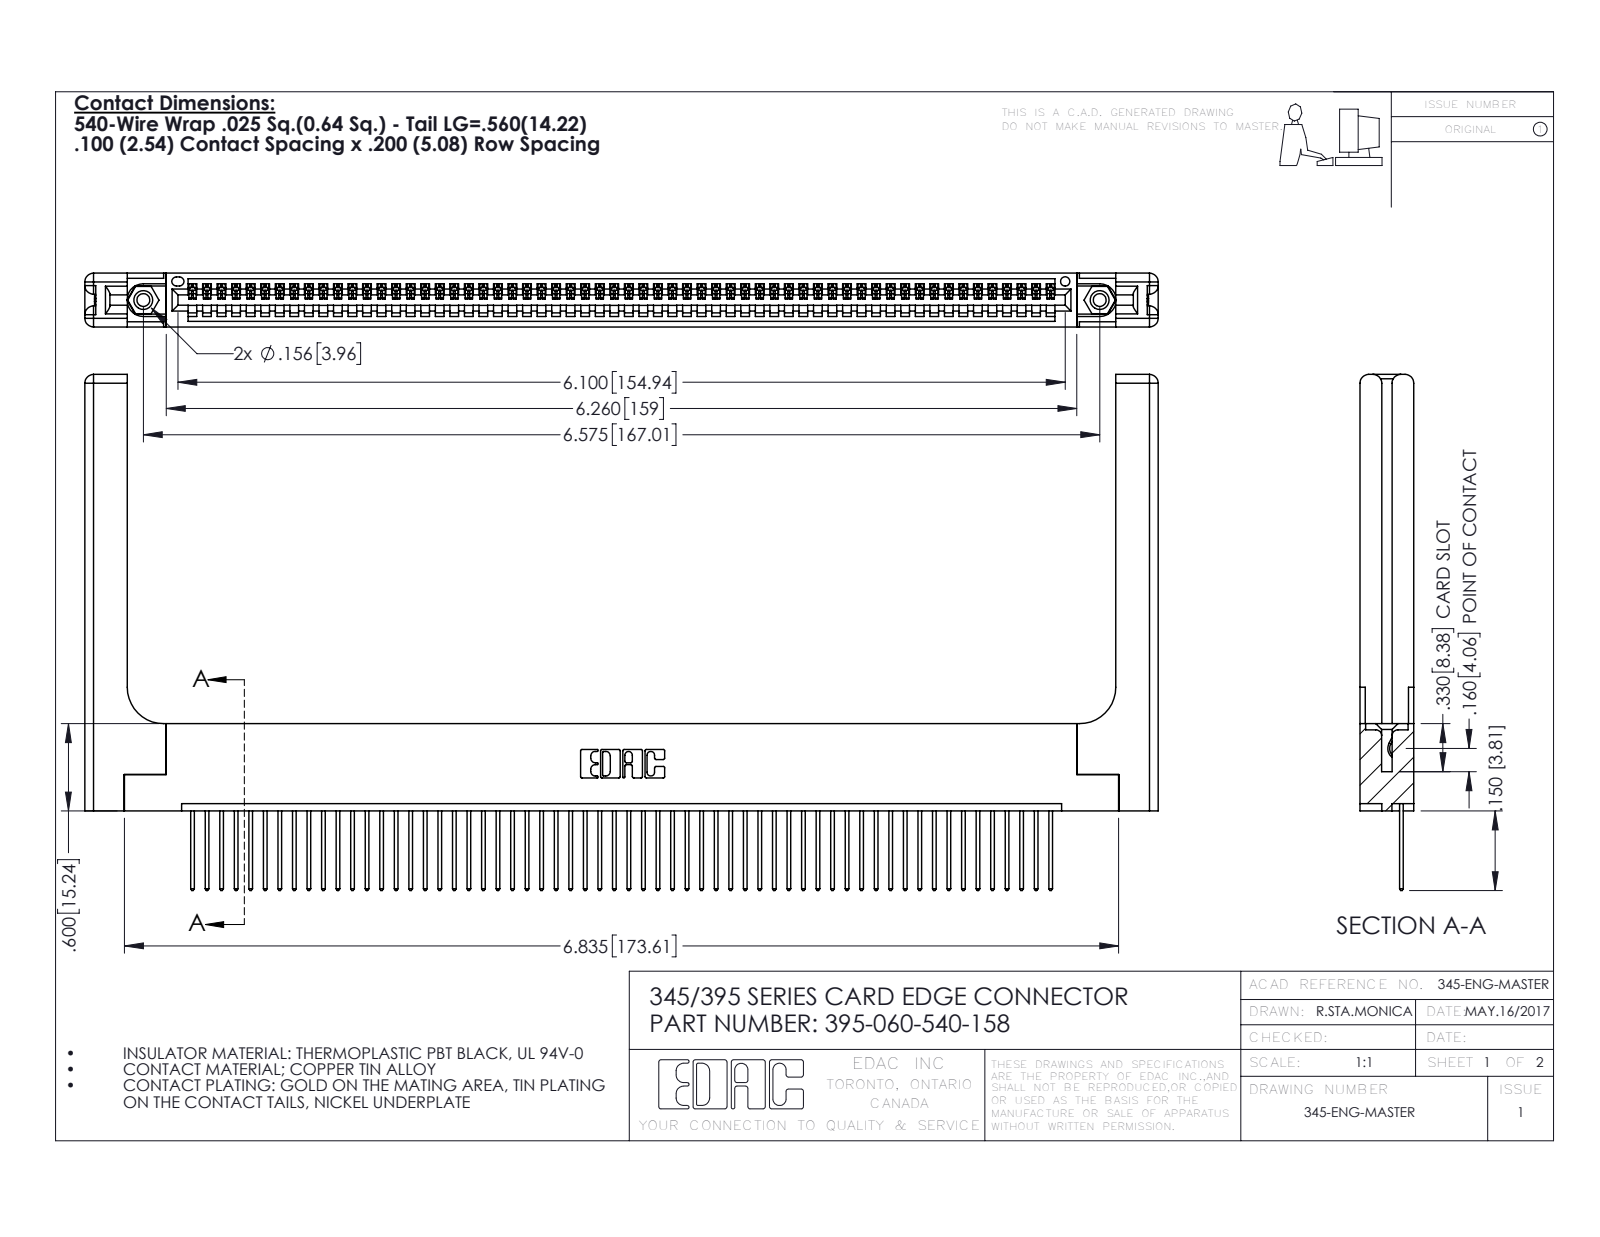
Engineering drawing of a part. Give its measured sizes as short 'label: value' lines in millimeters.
name: 345 Part_Flush Mounting Lugs - 0.156 Dia-TH; 345-292-001_345-293-140; 395-060-540-158; 345-250-001_345-250-001-102 (+1 more)
written by: SolidWorks 2016 (CONFIG_CONTROL_DESIGN)
unit: mm
bodies: 65 solids, 3862 faces (2628 planar, 1174 cylindrical, 60 other)
size: 187.4 × 90.1 × 9.4
volume: 26 530 mm³; area: 30 100 mm²
holes: 2× ⌀2.3, 2× ⌀3.2, 2× ⌀4, 1× ⌀1.6
bosses: 2× ⌀3.9
rounds: 120× R0.2, 120× R0.3, 22× R0.3, 16× R1.5, 6× R0.2, 6× R0.8, 3× R0.7, 2× R0.8
face distances: 1.8, 7.6, 9.4, 2.5, 6.9, 0.6, 5.1, 5.7, 3.8, 3.8
hole spacings: 6.9, 161, 167
